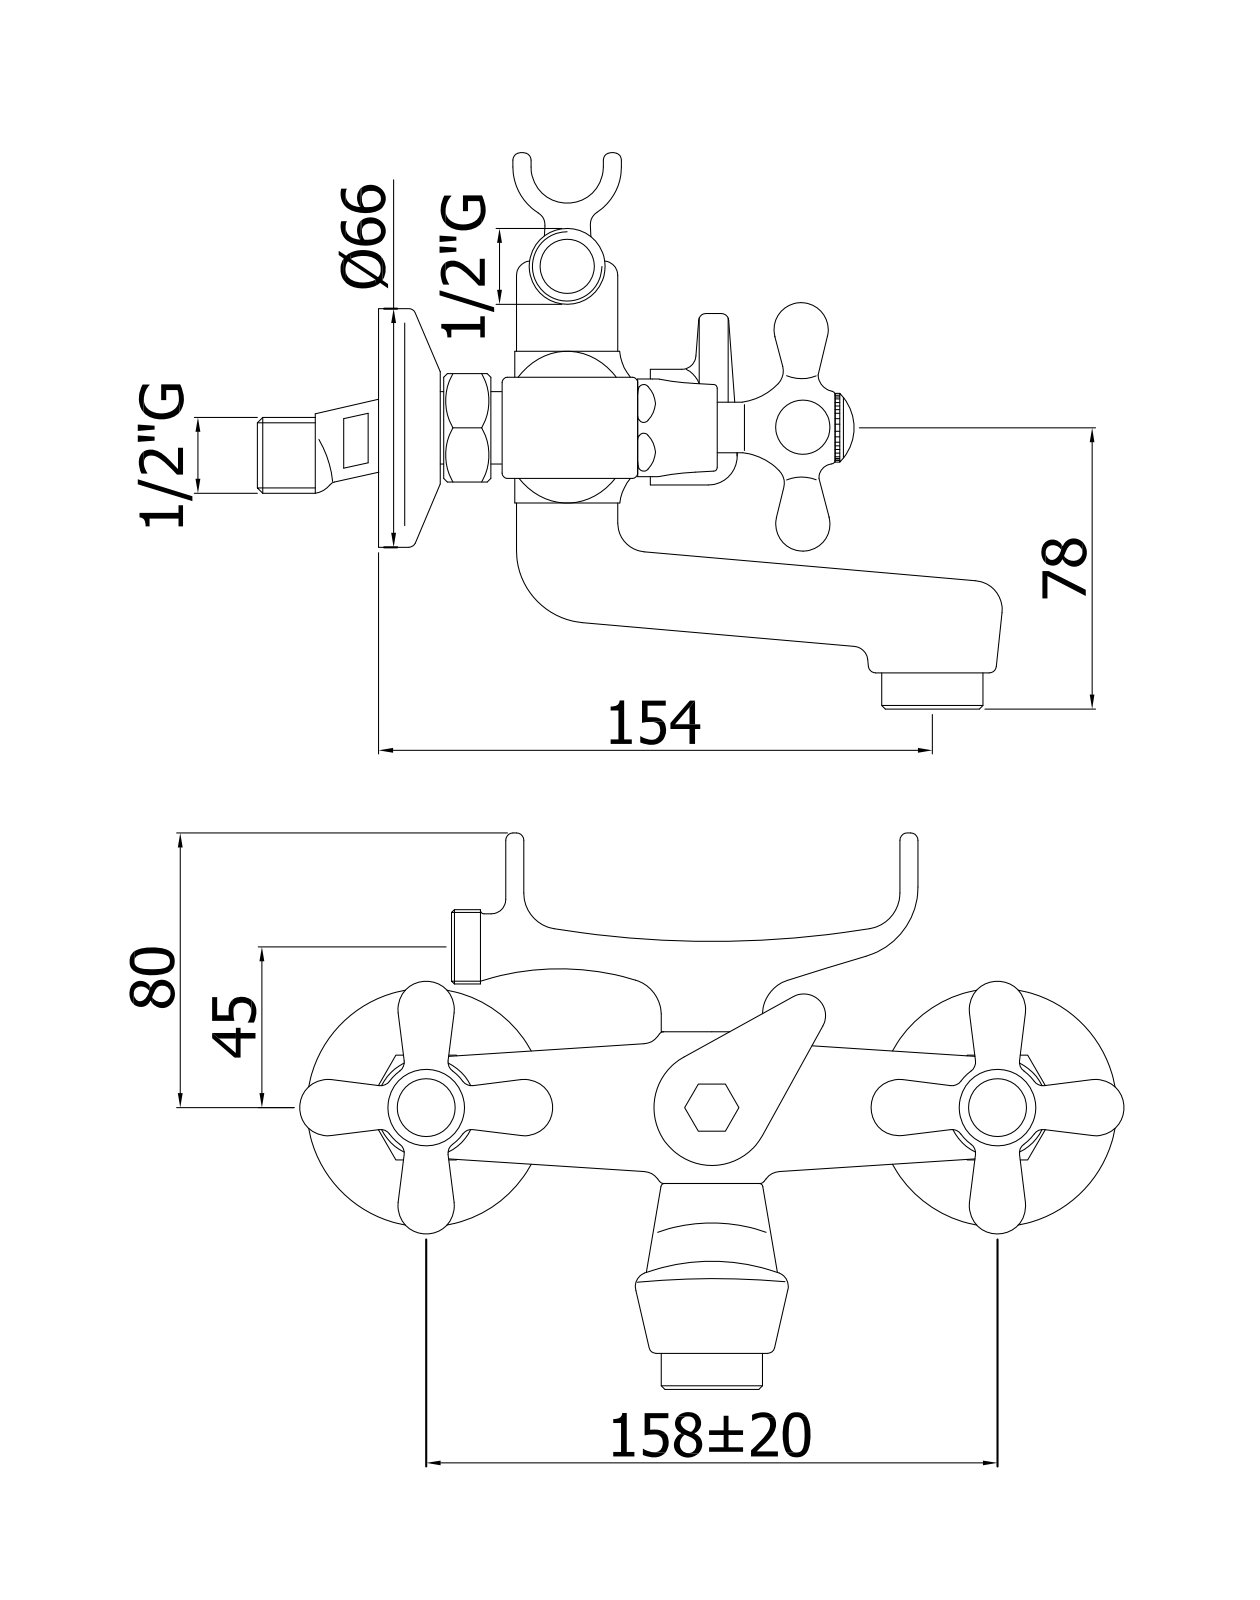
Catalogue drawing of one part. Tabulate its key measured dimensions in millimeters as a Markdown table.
| quantity | value |
| --- | --- |
| part name | IRV024CR |
| STEP written by | CREO PARAMETRIC BY PTC INC, 2020044 (CONFIG_CONTROL_DESIGN) |
| units | millimeters |
| bodies | 2 solids, 655 faces (99 planar, 142 cylindrical, 414 other) |
| overall size | 293.71 × 159.25 × 156 |
| volume | 616 768 mm³ |
| surface area | 114 052 mm² |
| round bosses / shafts (diameter × count) | 20.5 × 3, 65.5 × 2, 27.5 × 2, 18 × 2, 13.5 × 2, 53.5 × 1, 31.5 × 1, 28.5 × 1 |
| partial cylindrical surfaces (radius × count) | 3 × 24, 10 × 8, 1.5 × 4, 5 × 4, 6 × 3, 14.5 × 2, 15 × 2, 15.5 × 2 |
| main face-to-face distances | 1.75, 13, 29, 11.25, 108, 103.2, 34, 26.5, 69.2, 79 |
